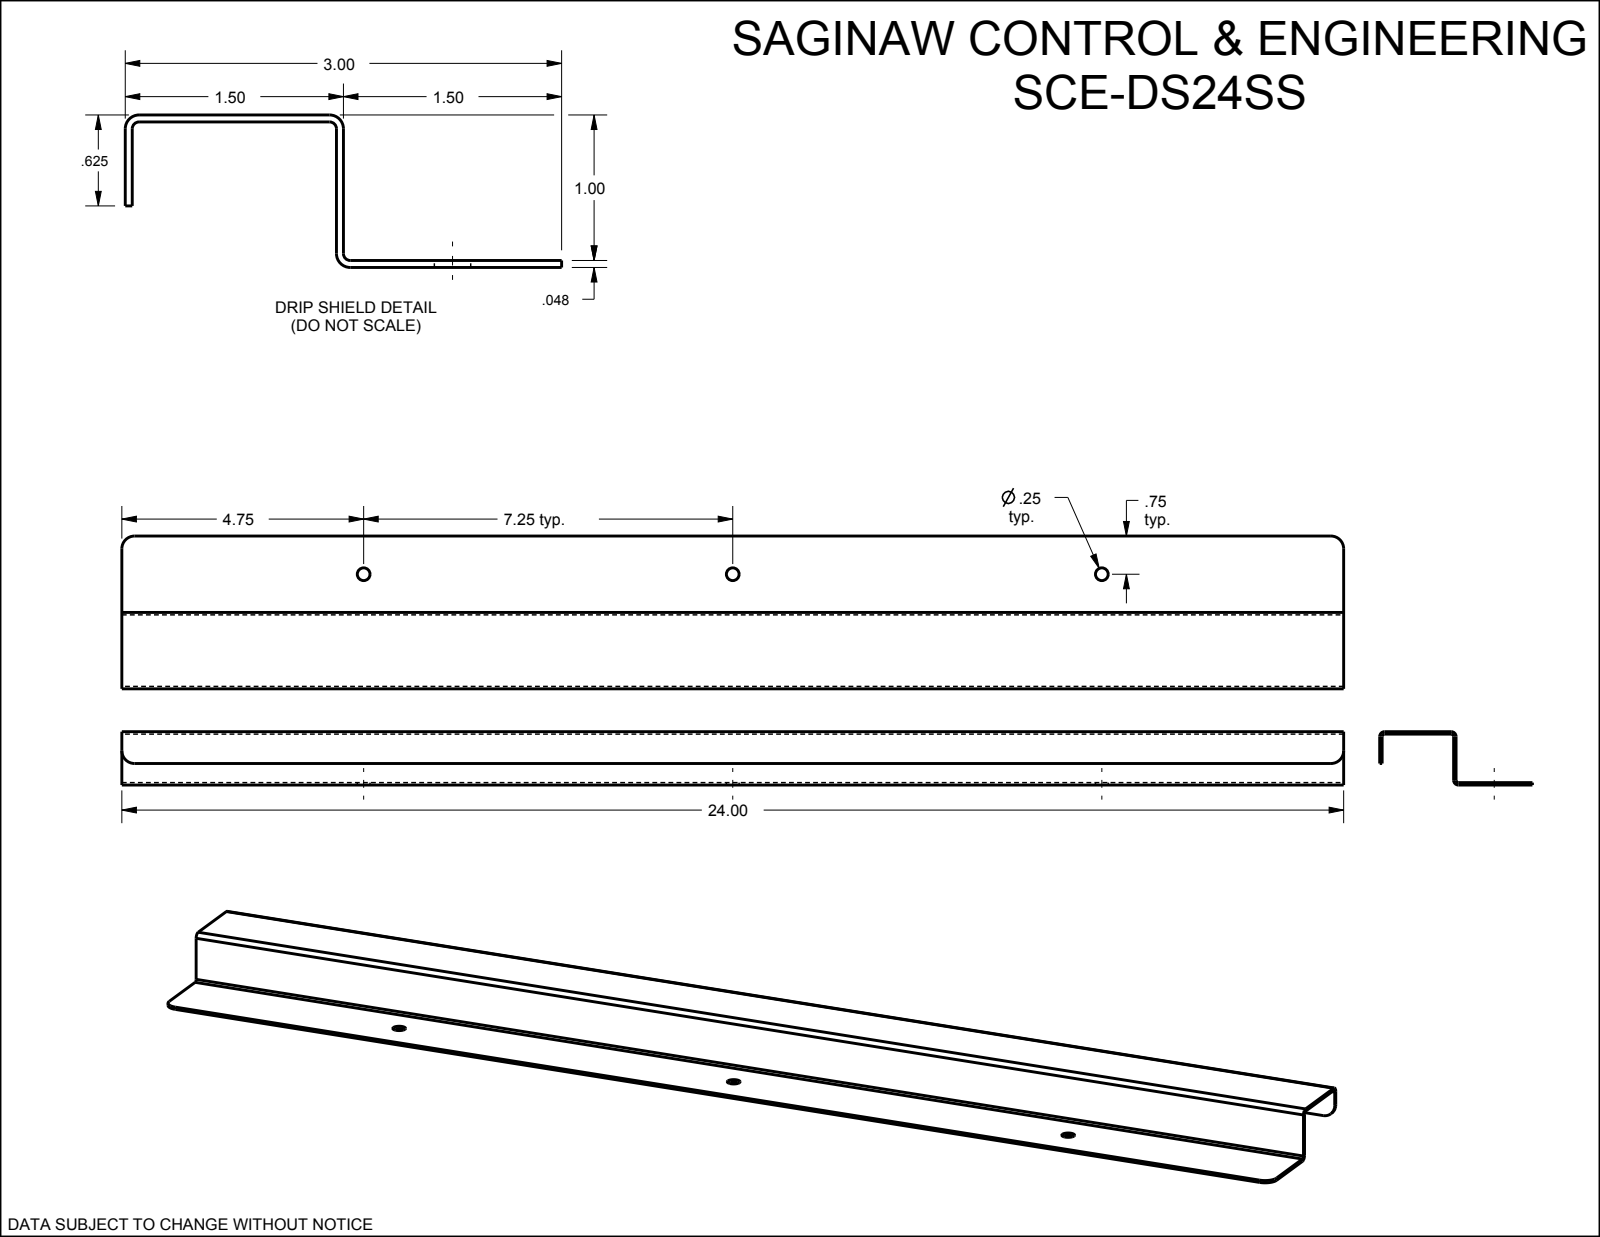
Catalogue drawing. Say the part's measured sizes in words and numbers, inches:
The part is named "SCE-DS24SS6". Its 3-D file was written by "SolidWorks 2019 (CONFIG_CONTROL_DESIGN)". It is 1 solid with 25 faces: 12 planar, 13 cylindrical and 0 other. Overall it measures 24 by 3 by 1.048 inches. Its volume is 5.158 cubic inches and its surface area 217.7 square inches. Round holes: 3 of diameter 0.25. Partial cylindrical surfaces (rounded edges, fillets, slot ends): 4 of radius 0.25, 3 of radius 0.047, 3 of radius 0.095. The main face-to-face distances are 0.048, 1, 1.048, 0.952, 1.452, 1.5, 1.404, 0.423, 0.375, 0.577. The hole center spacings are 7.25, 14.5.
